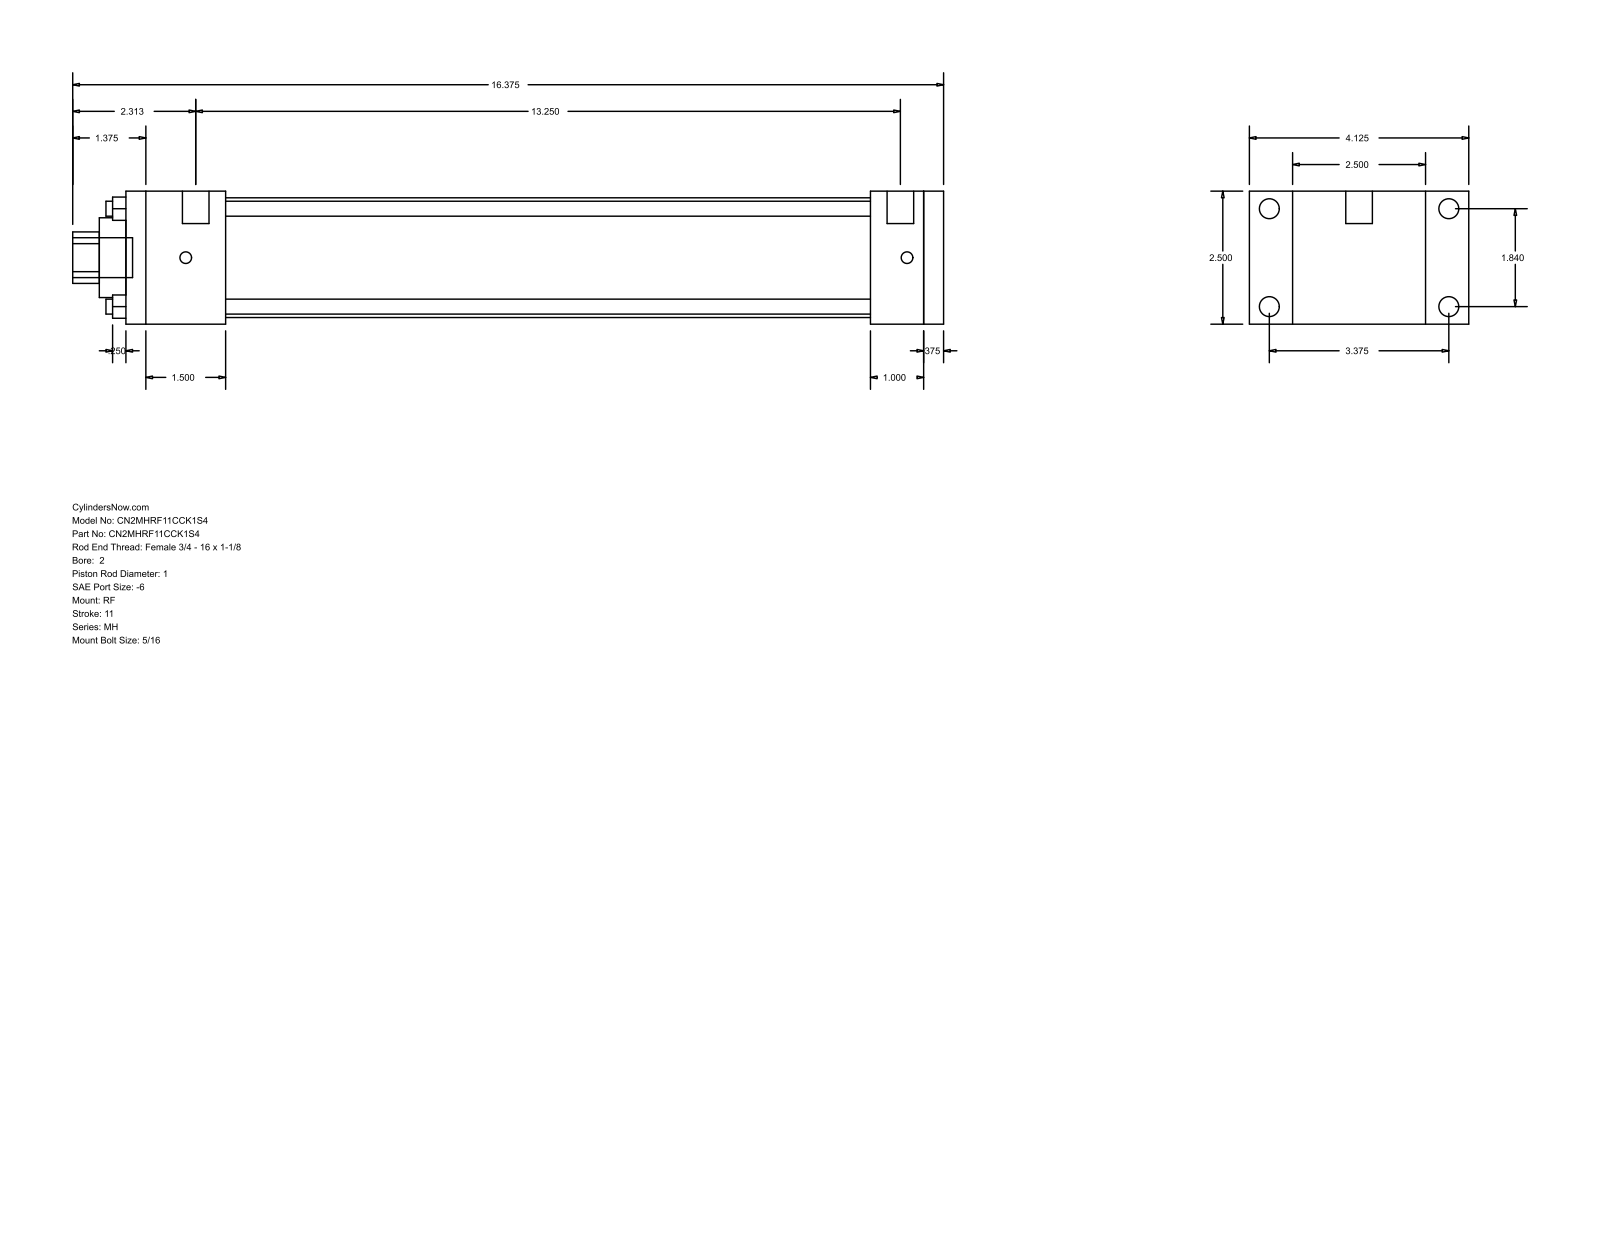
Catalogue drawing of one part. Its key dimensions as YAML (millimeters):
part_name: "MH_RF__0200_1"
step_written_by: "GSSL Pune (CONFIG_CONTROL_DESIGN)"
units: millimeters
bodies: {solids: 0, faces: 92, planar: 64, cylindrical: 28, other: 0}
overall_size: [415.93, 104.78, 63.5]
round_holes:
  - {diameter: 7.14, count: 4}
  - {diameter: 25.4, count: 1}
  - {diameter: 38.1, count: 1}
  - {diameter: 57.15, count: 1}
round_bosses_or_shafts:
  - {diameter: 9.53, count: 4}
  - {diameter: 5.56, count: 4}
  - {diameter: 12.7, count: 2}
  - {diameter: 19.05, count: 1}
partial_cylinders:
  - {radius: 12.29, count: 1}
face_to_face_distances: [63.5, 390.53, 381, 9.53, 20.64, 25.4, 47.63, 355.6, 307.97, 333.37]
hole_center_spacings: [33.05, 46.74, 66.1]
